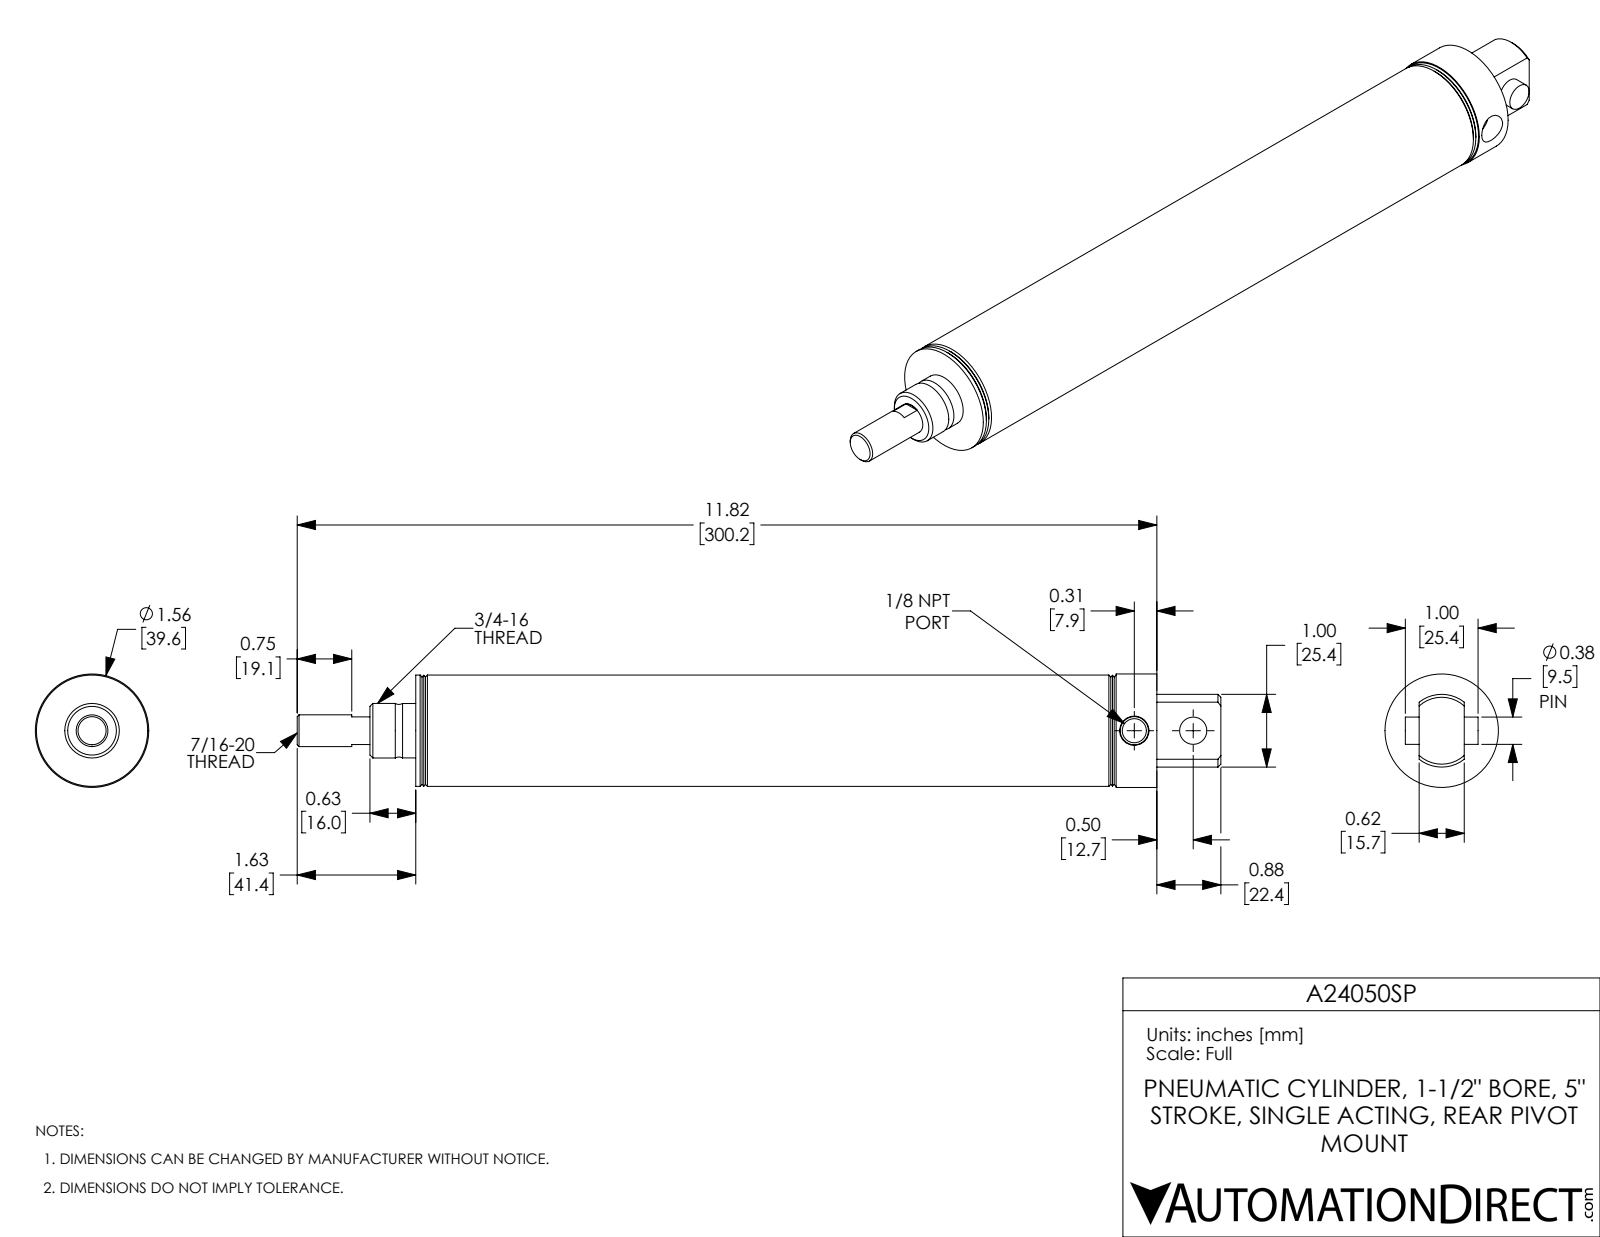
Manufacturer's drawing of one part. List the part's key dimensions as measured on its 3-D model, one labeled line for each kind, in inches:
Part name (STEP PRODUCT): A24050SP-Rod; A24050SP-MainBody; A24050SP; A24050SP-PIN
STEP written by: SolidWorks 2017 (AUTOMOTIVE_DESIGN)
Units: inches
Bodies: 3 solids, 78 faces (22 planar, 26 cylindrical, 30 other)
Overall size (bounding box): 12.7 × 1.56 × 1.56
Volume: 11.6 in³ · Surface area: 110.6 in²
Round holes (diameter × count): ⌀0.332 ×1, ⌀0.375 ×1, ⌀0.437 ×1, ⌀1.5 ×1
Round bosses / shafts (diameter × count): ⌀1.56 ×1, ⌀1.53 ×1, ⌀0.75 ×1, ⌀0.747 ×1
Partial cylindrical surfaces — rounded edges, fillets, slot ends (radius × count): R0.5 ×1
Main face-to-face distances: 0.5, 5.5, 5, 7.69, 7.19, 2.19, 2.5, 3, 8, 10.19
Hole centre spacings: 0.81
